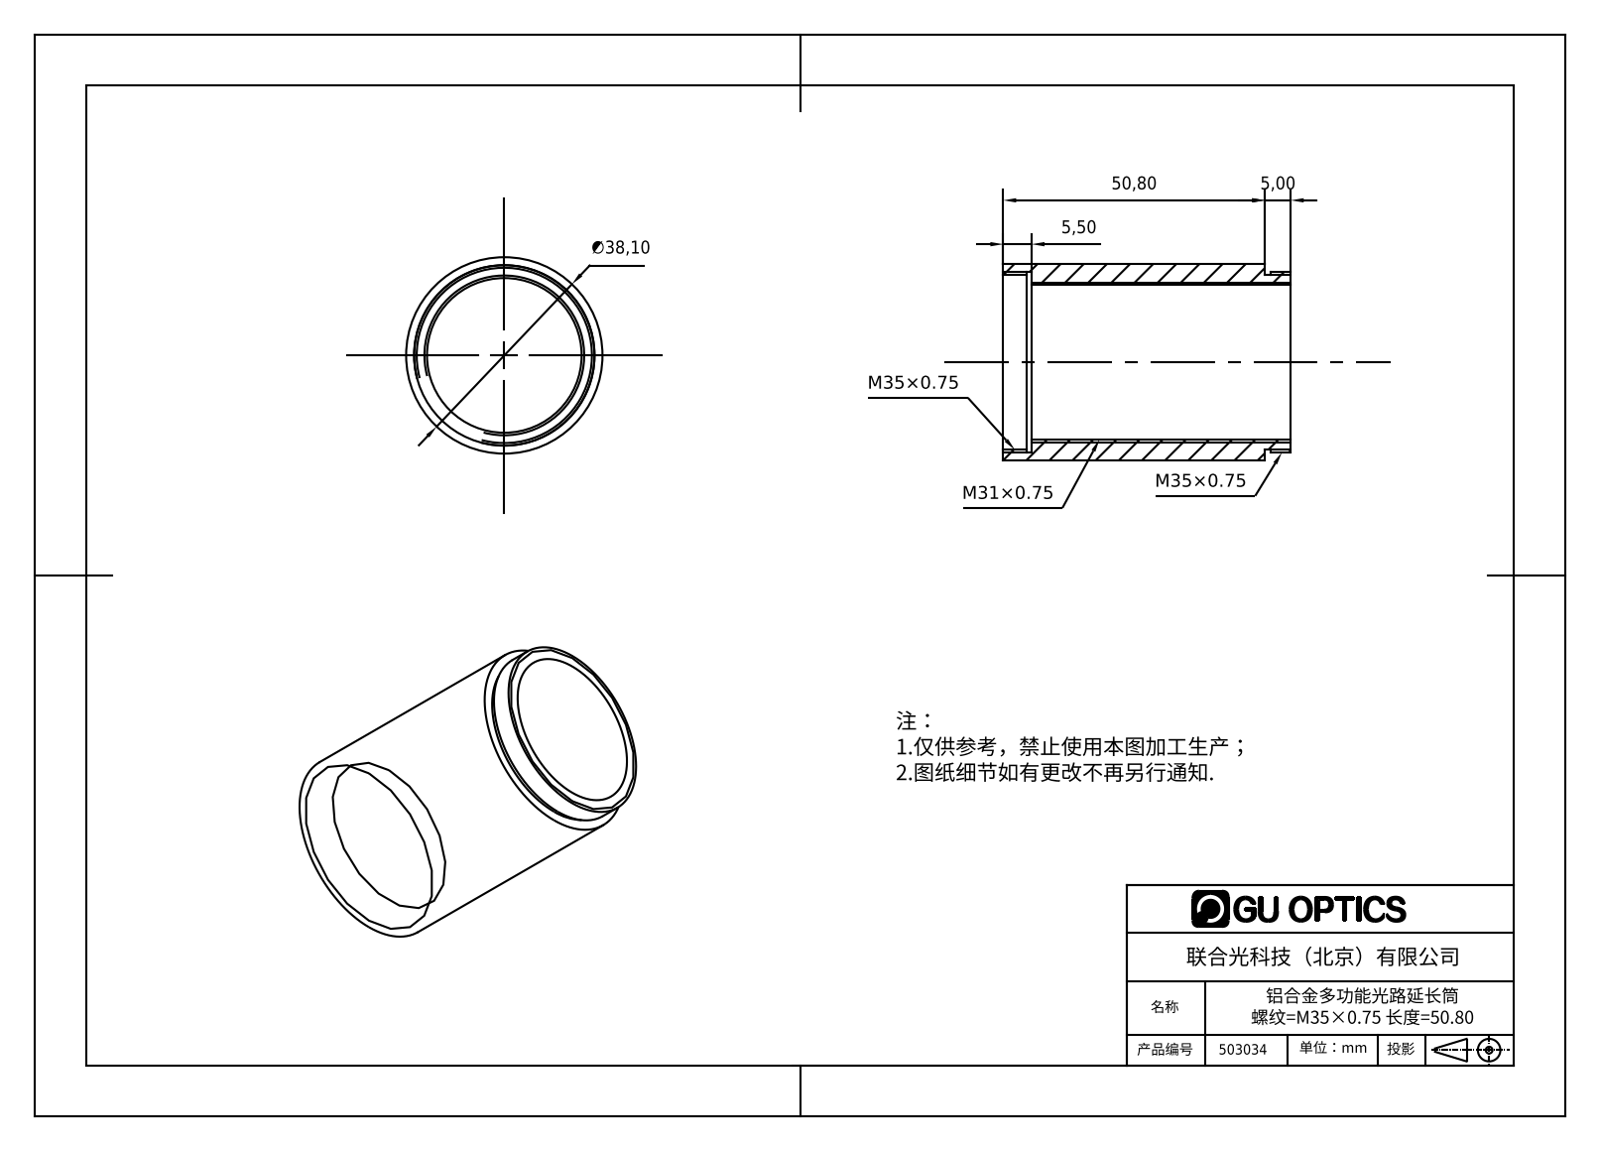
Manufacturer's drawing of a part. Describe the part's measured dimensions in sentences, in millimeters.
The part is named "503034". Its 3-D file was written by "SolidWorks 2016 (AUTOMOTIVE_DESIGN)". It is 1 solid with 18 faces: 6 planar, 12 cylindrical and 0 other. Overall it measures 55.8 by 38.1 by 38.1 millimeters. Its volume is 22 059 cubic millimeters and its surface area 13 064 square millimeters. Round holes: 1 of diameter 30, 1 of diameter 34, 1 of diameter 35.2. Round bosses or shafts: 1 of diameter 38.1, 1 of diameter 35. The main face-to-face distances are 50.3, 45.3, 5, 5.5, 50.8, 55.8, 1, 46.3, 4.5, 51.3.
